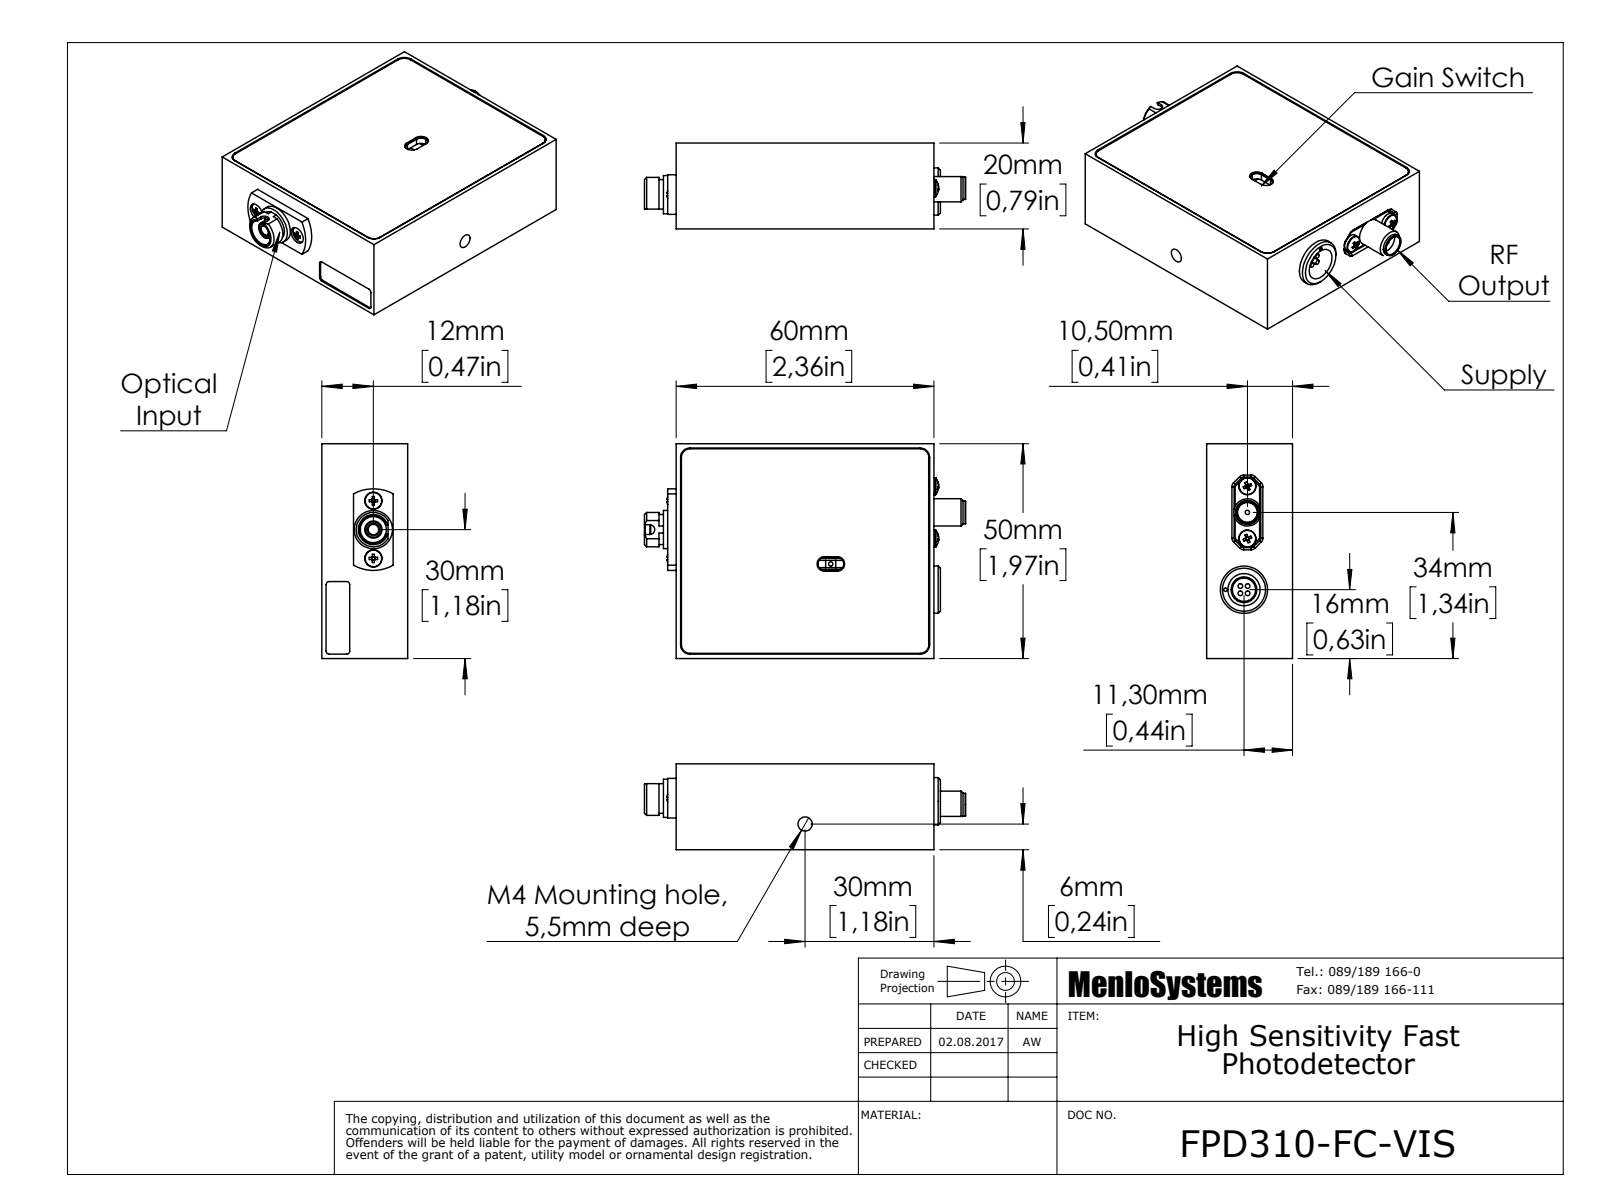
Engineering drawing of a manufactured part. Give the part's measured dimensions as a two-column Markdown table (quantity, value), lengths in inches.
| quantity | value |
| --- | --- |
| part name | FPD310-FC-VIS_170721 |
| STEP written by | SolidWorks 2016 (AUTOMOTIVE_DESIGN) |
| units | inches |
| bodies | 21 solids, 1109 faces (472 planar, 298 cylindrical, 339 other) |
| overall size | 2.945 × 1.969 × 0.787 |
| volume | 2.376 in³ |
| surface area | 44.39 in² |
| round holes (diameter × count) | 0.063 × 23, 0.087 × 12, 0.157 × 12, 0.102 × 2, 0.031 × 1, 0.039 × 1, 0.096 × 1, 0.126 × 1, 0.13 × 1, 0.181 × 1, 0.239 × 1, 0.295 × 1 |
| round bosses / shafts (diameter × count) | 0.079 × 14, 0.15 × 10, 0.157 × 4, 0.043 × 4, 0.018 × 3, 0.433 × 1, 0.354 × 1, 0.352 × 1 |
| partial cylindrical surfaces (radius × count) | 0.087 × 26, 0.028 × 8, 0.031 × 8, 0.079 × 8, 0.055 × 4, 0.059 × 2, 0.067 × 2, 0.044 × 1 |
| main face-to-face distances | 0.059, 0.77, 0.014, 0.711, 0.073, 0.783, 0.256, 0.276, 1.969, 0.508 |
| hole center spacings | 0.166, 0.365, 0.413, 0.589, 0.65, 0.762, 0.787, 0.859 |
